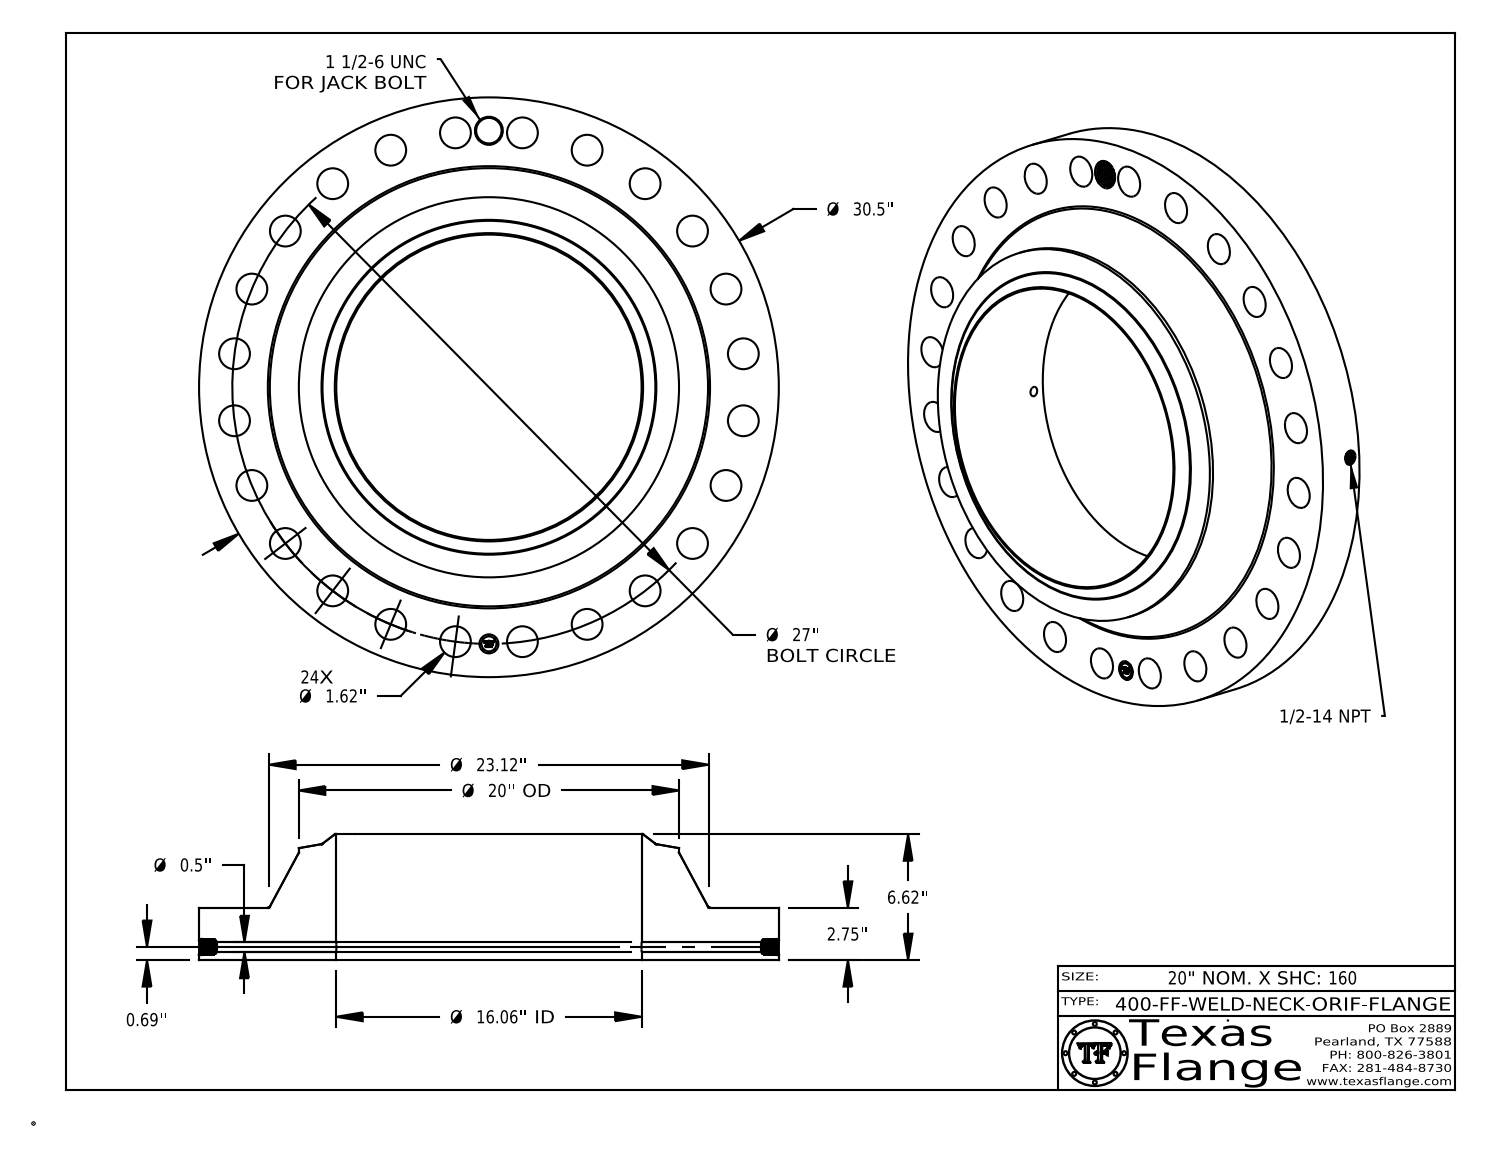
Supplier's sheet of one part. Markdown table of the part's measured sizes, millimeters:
| quantity | value |
| --- | --- |
| part name | 400-FF-WELD-NECK |
| STEP written by | CATIA V5 STEP AP214 (AUTOMOTIVE_DESIGN) |
| units | millimeters |
| bodies | 1 solid, 811 faces (368 planar, 127 cylindrical, 316 other) |
| overall size | 774.7 × 774.7 × 168.1 |
| volume | 30 090 000 mm³ |
| surface area | 1 337 000 mm² |
| round holes (diameter × count) | 41.1 × 24, 12.7 × 1, 17.1 × 1, 25.4 × 1, 34.1 × 1, 408 × 1 |
| round bosses / shafts (diameter × count) | 1.5 × 8, 774.7 × 1, 508 × 1, 20 × 1 |
| main face-to-face distances | 69.9, 168.1, 98.3, 69.5, 0.4, 98.7, 7.6, 7.4, 1.4, 6.3 |
| hole center spacings | 342.9, 593.9, 633.6, 544.1, 89.5, 177.5, 484.9, 662.4 |
